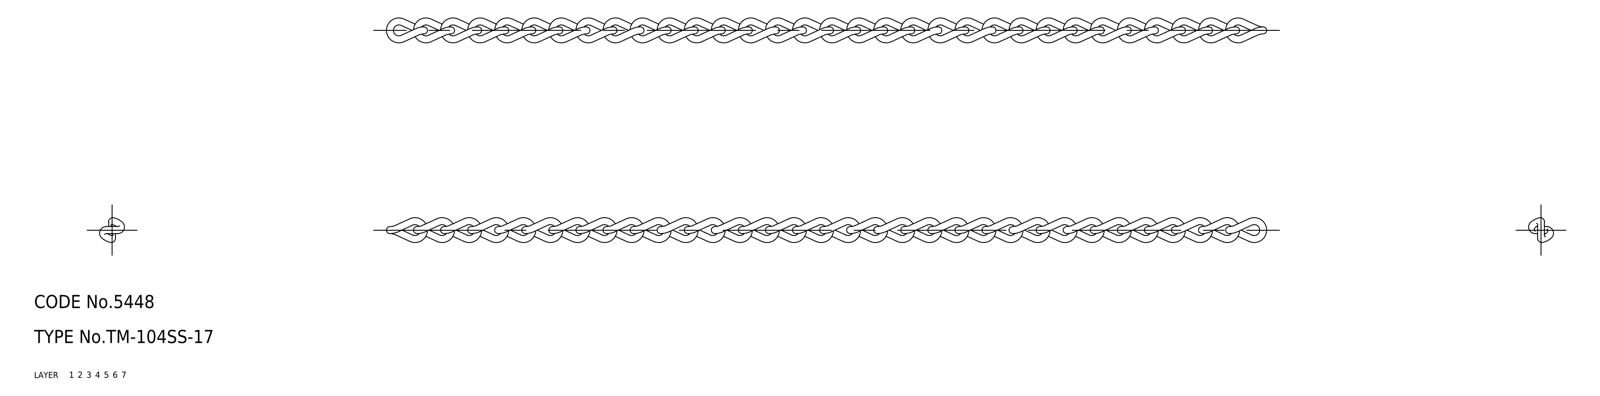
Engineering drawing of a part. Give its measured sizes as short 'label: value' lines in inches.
name: chain; TM_104SS_17_10120_36
written by: CADfix (AUTOMOTIVE_DESIGN)
unit: in
bodies: 32 solids, 768 faces (0 planar, 0 cylindrical, 768 other)
size: 7.937 × 0.224 × 0.224
volume: 0.086 in³; area: 5.461 in²
